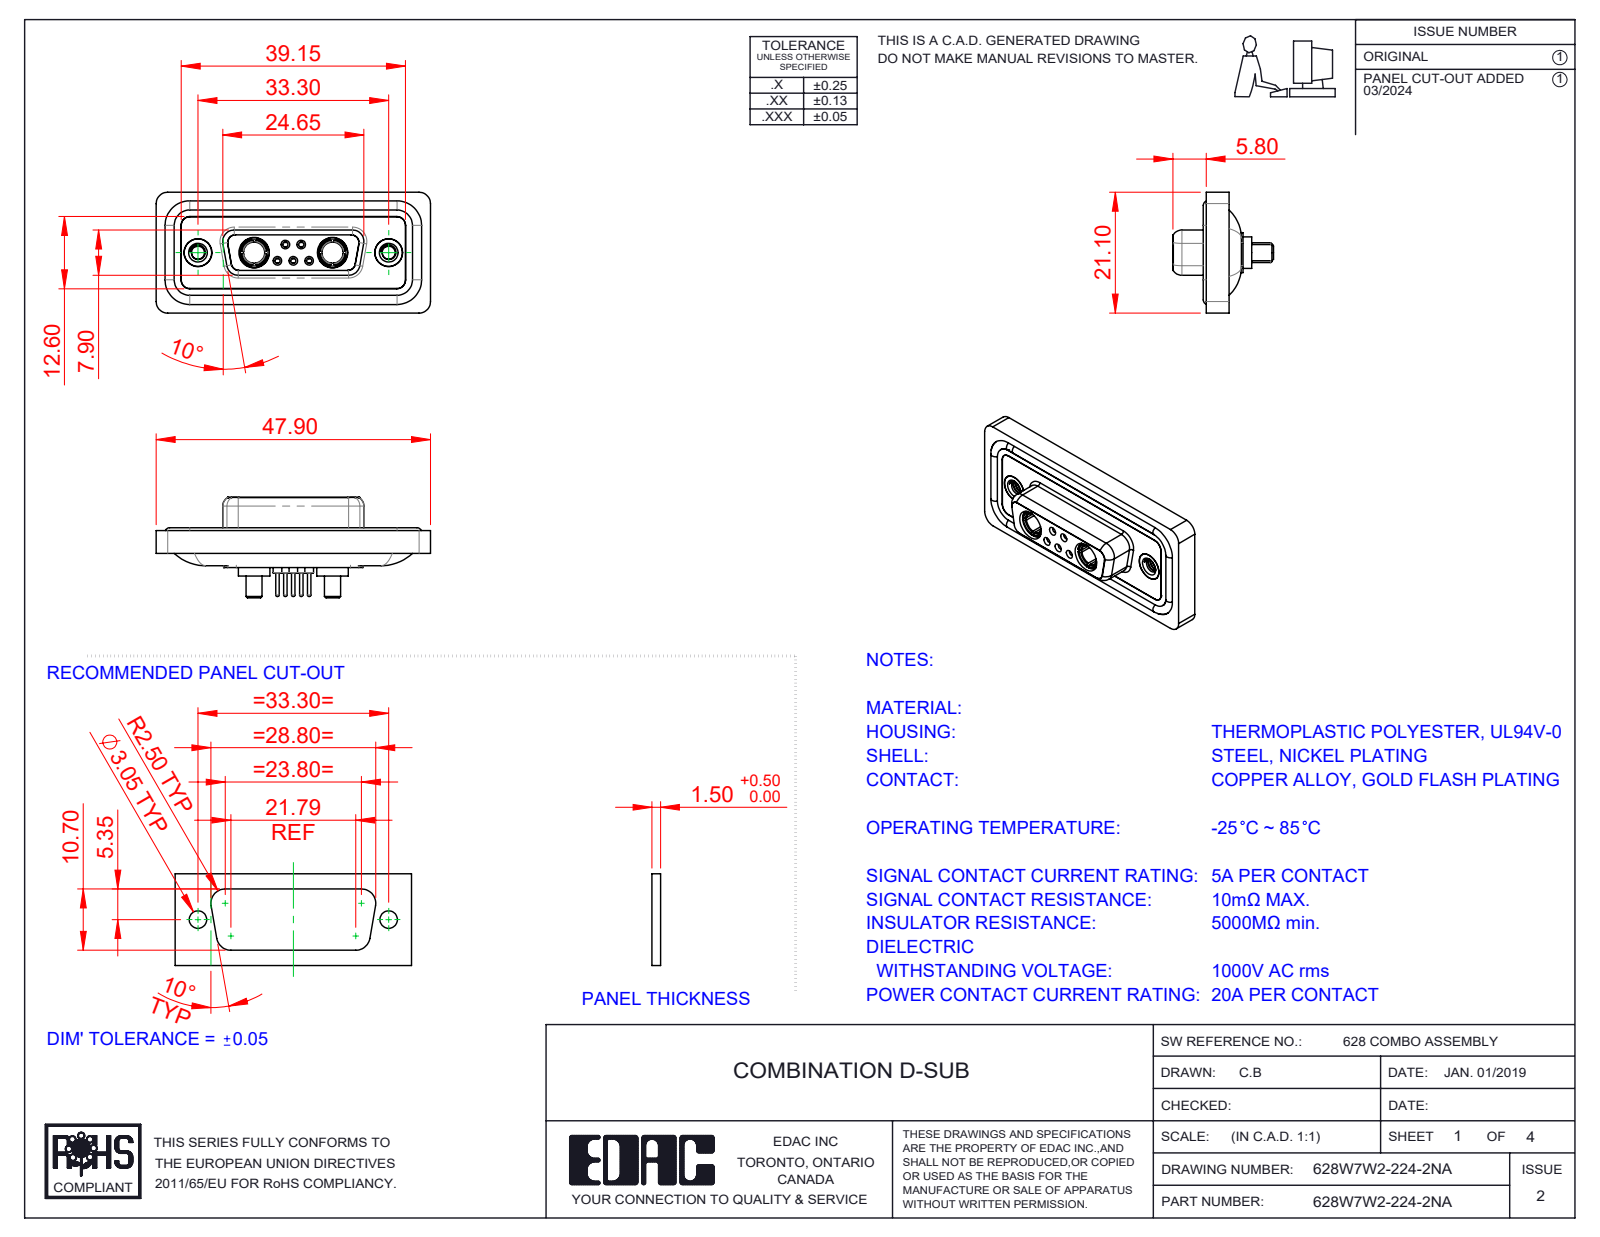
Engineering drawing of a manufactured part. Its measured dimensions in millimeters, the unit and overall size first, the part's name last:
Units: millimetres
Overall size (bounding box): 47.9 × 21.1 × 17.55
Round holes (diameter × count): ⌀0.9 ×5, ⌀1.1 ×5, ⌀1.5 ×5, ⌀2 ×5, ⌀4.85 ×4, ⌀1.6 ×3, ⌀1.7 ×2, ⌀2.26 ×2, ⌀3.7 ×2, ⌀4 ×2, ⌀4.05 ×2, ⌀5 ×2
Round bosses / shafts (diameter × count): ⌀1.6 ×6, ⌀2.2 ×5, ⌀0.6 ×5, ⌀5.5 ×2, ⌀5.2 ×2, ⌀4.96 ×2, ⌀4.95 ×2, ⌀4.8 ×2
Partial cylindrical surfaces — rounded edges, fillets, slot ends (radius × count): R1.5 ×22, R2 ×20, R1.35 ×12, R1.6 ×8, R0.25 ×4, R0.5 ×4, R0.6 ×4, R0.65 ×4
Main face-to-face distances: 0.4, 1.8, 1.6, 0.5, 2.9, 7.45, 1.1, 5.65, 6.6, 7.05
Hole centre spacings: 3.16, 2.77, 9.8, 23.5, 4.31, 4.33, 5.03, 5.04
Volume: 6 079 mm³ · Surface area: 9 883 mm²
Bodies: 16 solids, 807 faces (238 planar, 331 cylindrical, 238 other)
Part name (STEP PRODUCT): Power Socket_20A S; 628Combo Contact Row 2_24; 628Combo Shell Front_15 Contacts; 628Combo Shell Rear_15 Contacts (+5 more)
STEP written by: SolidWorks 2023 (CONFIG_CONTROL_DESIGN)
